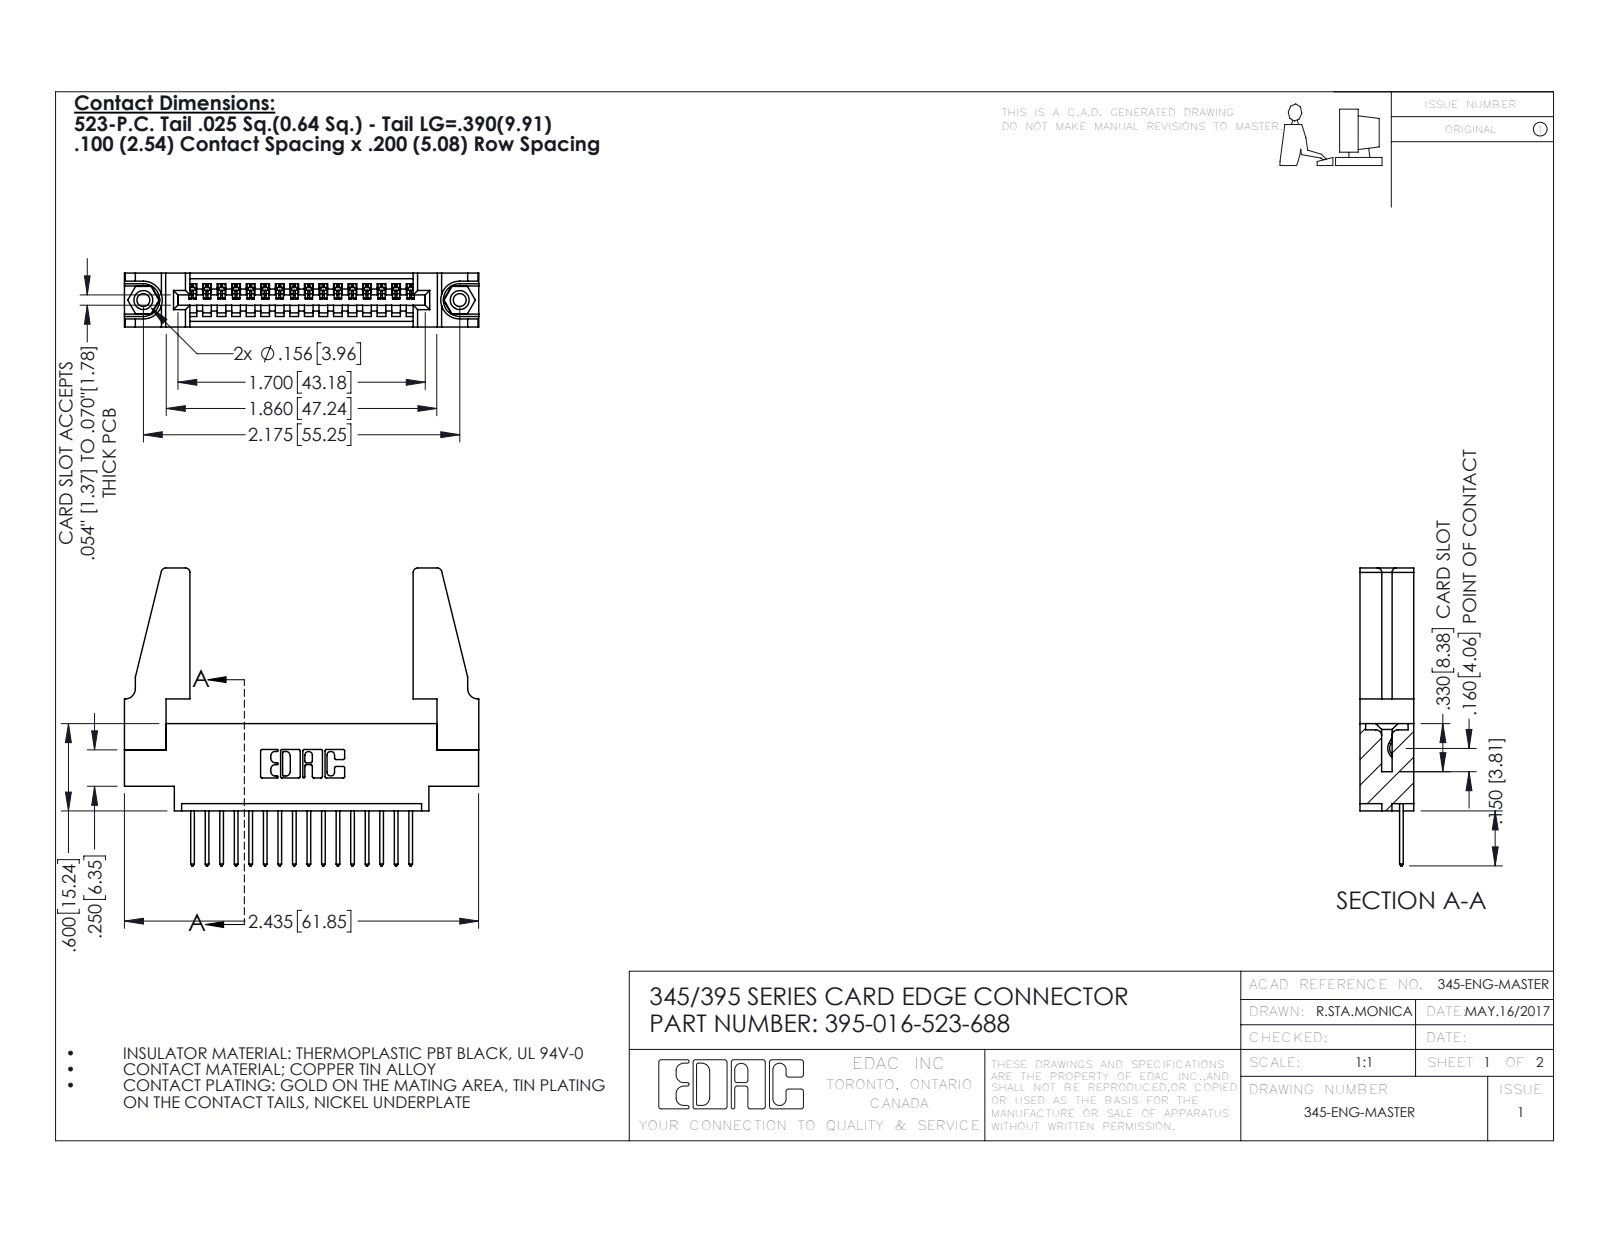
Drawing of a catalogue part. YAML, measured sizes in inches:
part_name: "345 Part_0.170 Offset - 0.156 Dia-TH; 345-292-001_345-293-123; 395-016-523-688; 345-220-078_345-220-088 (+1 more)"
step_written_by: "SolidWorks 2016 (CONFIG_CONTROL_DESIGN)"
units: inches
bodies: {solids: 21, faces: 1182, planar: 796, cylindrical: 370, other: 16}
overall_size: [2.436, 2.047, 0.37]
volume: 0.537
surface_area: 15.95
round_holes:
  - {diameter: 0.089, count: 2}
  - {diameter: 0.125, count: 2}
  - {diameter: 0.156, count: 2}
  - {diameter: 0.064, count: 1}
round_bosses_or_shafts:
  - {diameter: 0.155, count: 2}
partial_cylinders:
  - {radius: 0.006, count: 32}
  - {radius: 0.01, count: 32}
  - {radius: 0.01, count: 22}
  - {radius: 0.03, count: 8}
  - {radius: 0.007, count: 6}
  - {radius: 0.031, count: 6}
  - {radius: 0.026, count: 3}
  - {radius: 0.031, count: 2}
face_to_face_distances: [0.37, 0.072, 0.298, 0.2, 0.098, 0.272, 0.025, 0.225, 0.148, 0.15]
hole_center_spacings: [0.27, 1.942, 2.175]
